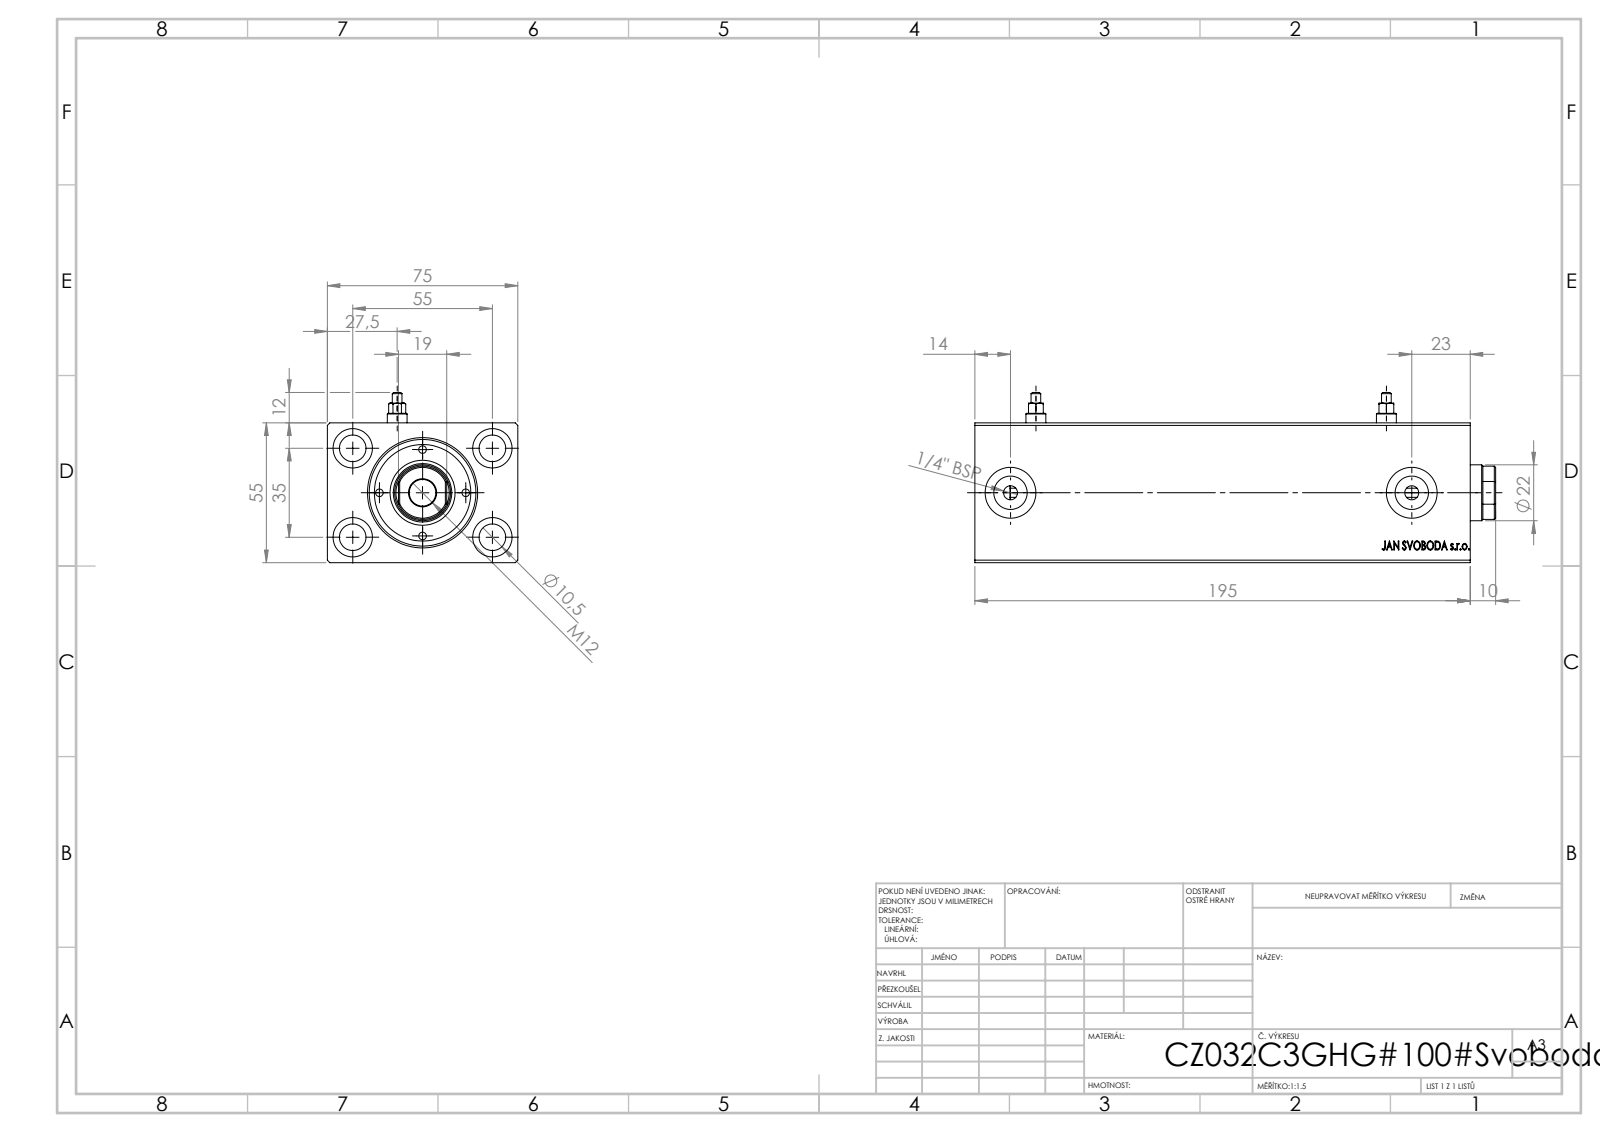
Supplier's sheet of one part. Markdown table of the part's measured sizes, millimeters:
| quantity | value |
| --- | --- |
| STEP written by | SolidWorks 2019 (CONFIG_CONTROL_DESIGN) |
| units | millimeters |
| bodies | 1 solid, 826 faces (398 planar, 46 cylindrical, 382 other) |
| overall size | 195 × 75 × 55 |
| volume | 572 051 mm³ |
| surface area | 104 838 mm² |
| round holes (diameter × count) | 10.5 × 4, 15.5 × 4, 5.5 × 2, 8 × 2, 13.16 × 2, 20 × 2, 32 × 1, 36 × 1, 42 × 1 |
| main face-to-face distances | 55, 75, 195, 13.6, 194.8, 10.33, 184.67, 181.2, 13.8, 10 |
| hole center spacings | 32.6, 35, 55, 65.19, 138, 158 |
